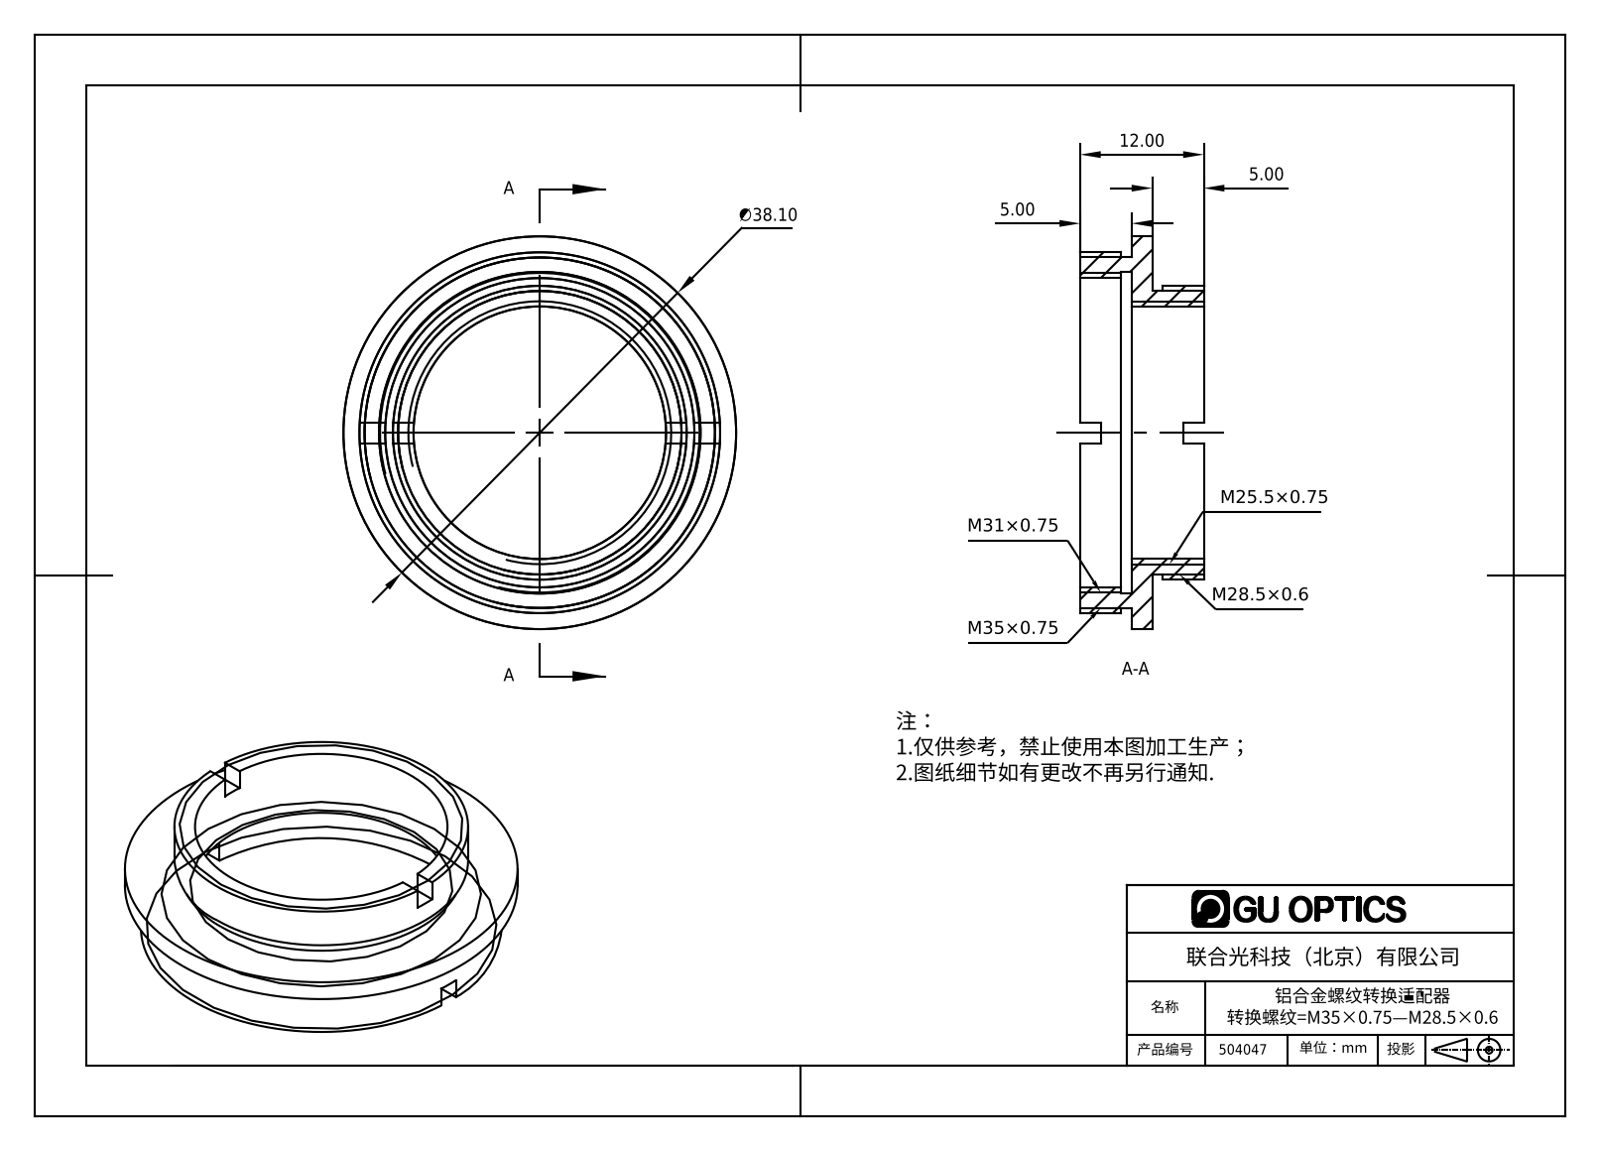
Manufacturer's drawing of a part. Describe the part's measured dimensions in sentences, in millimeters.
The part is named "504047". Its 3-D file was written by "SolidWorks 2016 (AUTOMOTIVE_DESIGN)". It is 1 solid with 38 faces: 22 planar, 16 cylindrical and 0 other. Overall it measures 38.1 by 38.1 by 12 millimeters. Its volume is 3 254 cubic millimeters and its surface area 3 897 square millimeters. Round holes: 1 of diameter 24.5, 1 of diameter 30, 1 of diameter 31.2. Round bosses or shafts: 1 of diameter 38.1, 1 of diameter 35, 1 of diameter 34, 1 of diameter 28.5, 1 of diameter 27.5. The main face-to-face distances are 2, 5, 7, 4, 3, 8, 12, 1, 10, 6.
